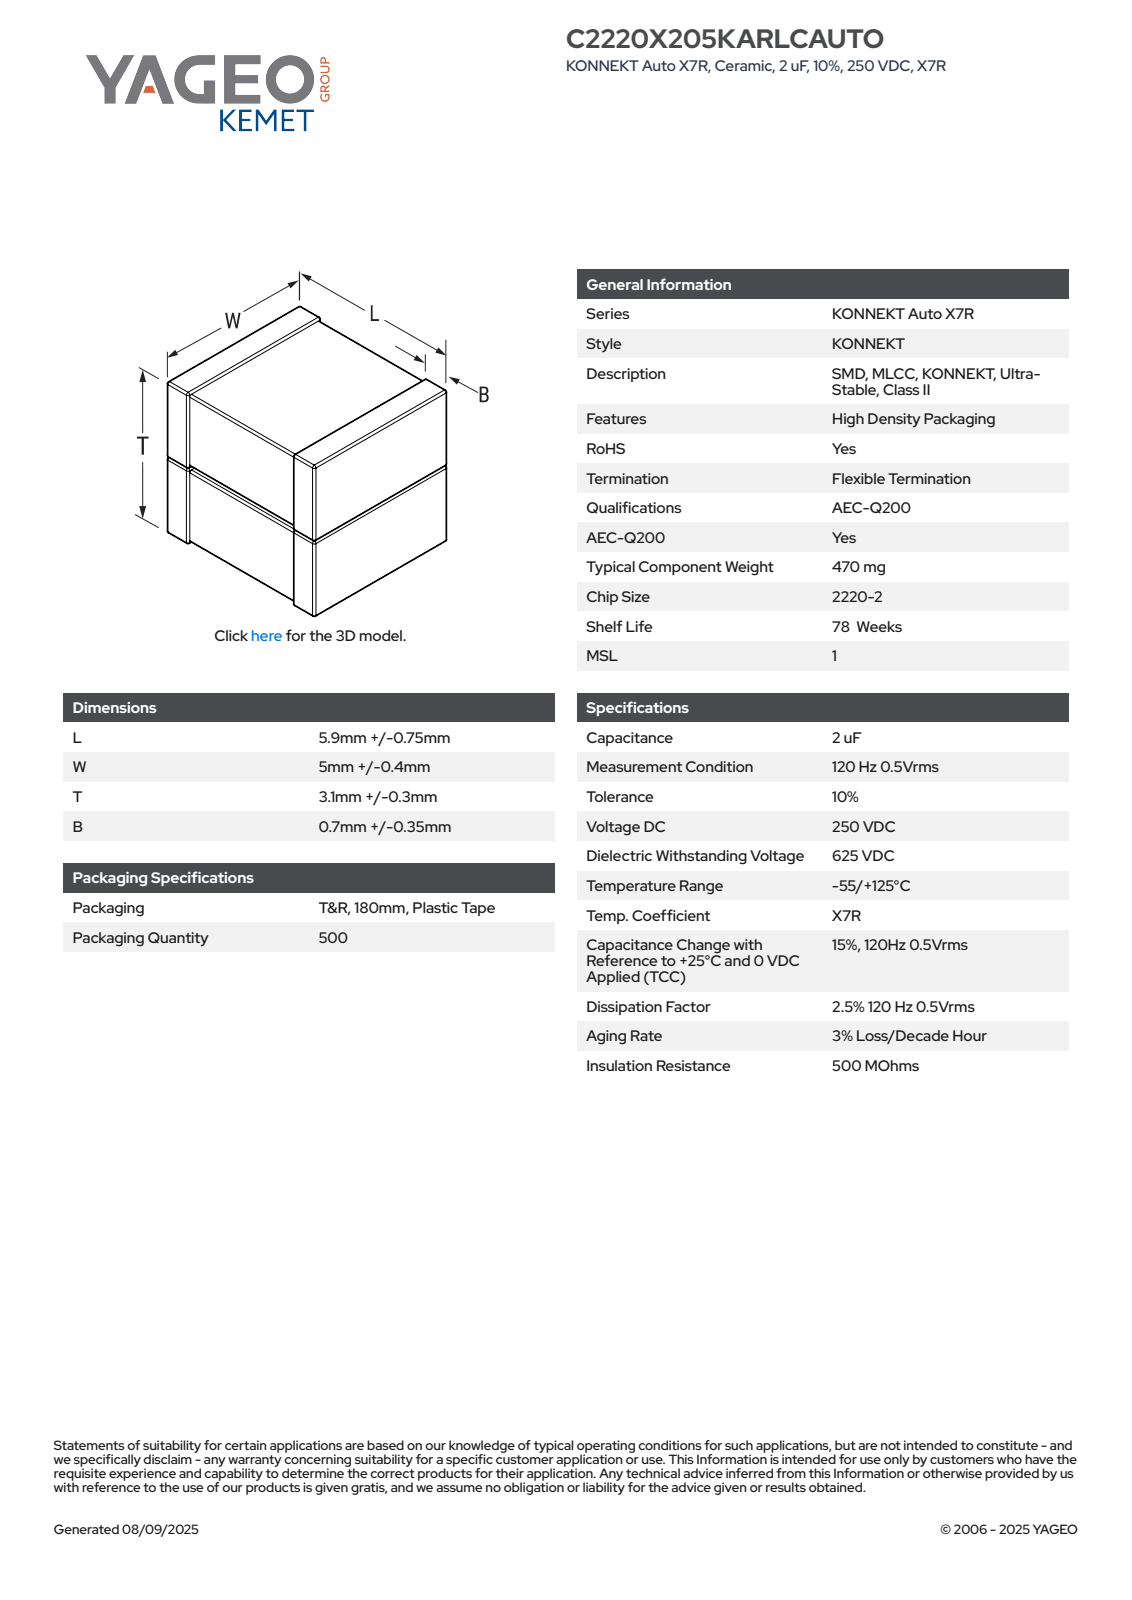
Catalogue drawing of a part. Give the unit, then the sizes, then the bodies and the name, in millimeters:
Units: millimetres
Overall size (bounding box): 6.65 × 5.4 × 3.4
Main face-to-face distances: 1.56, 1.7, 3.26, 1.77, 3.33, 1.63, 6.65, 5.26, 5.33, 3.4
Volume: 113 mm³ · Surface area: 203 mm²
Bodies: 4 solids, 197 faces (81 planar, 84 cylindrical, 32 other)
Part name (STEP PRODUCT): CCSS_K2T_2220-2_L6.65W5.4B1.05T3.4
STEP written by: SolidWorks 2020 (AUTOMOTIVE_DESIGN)
